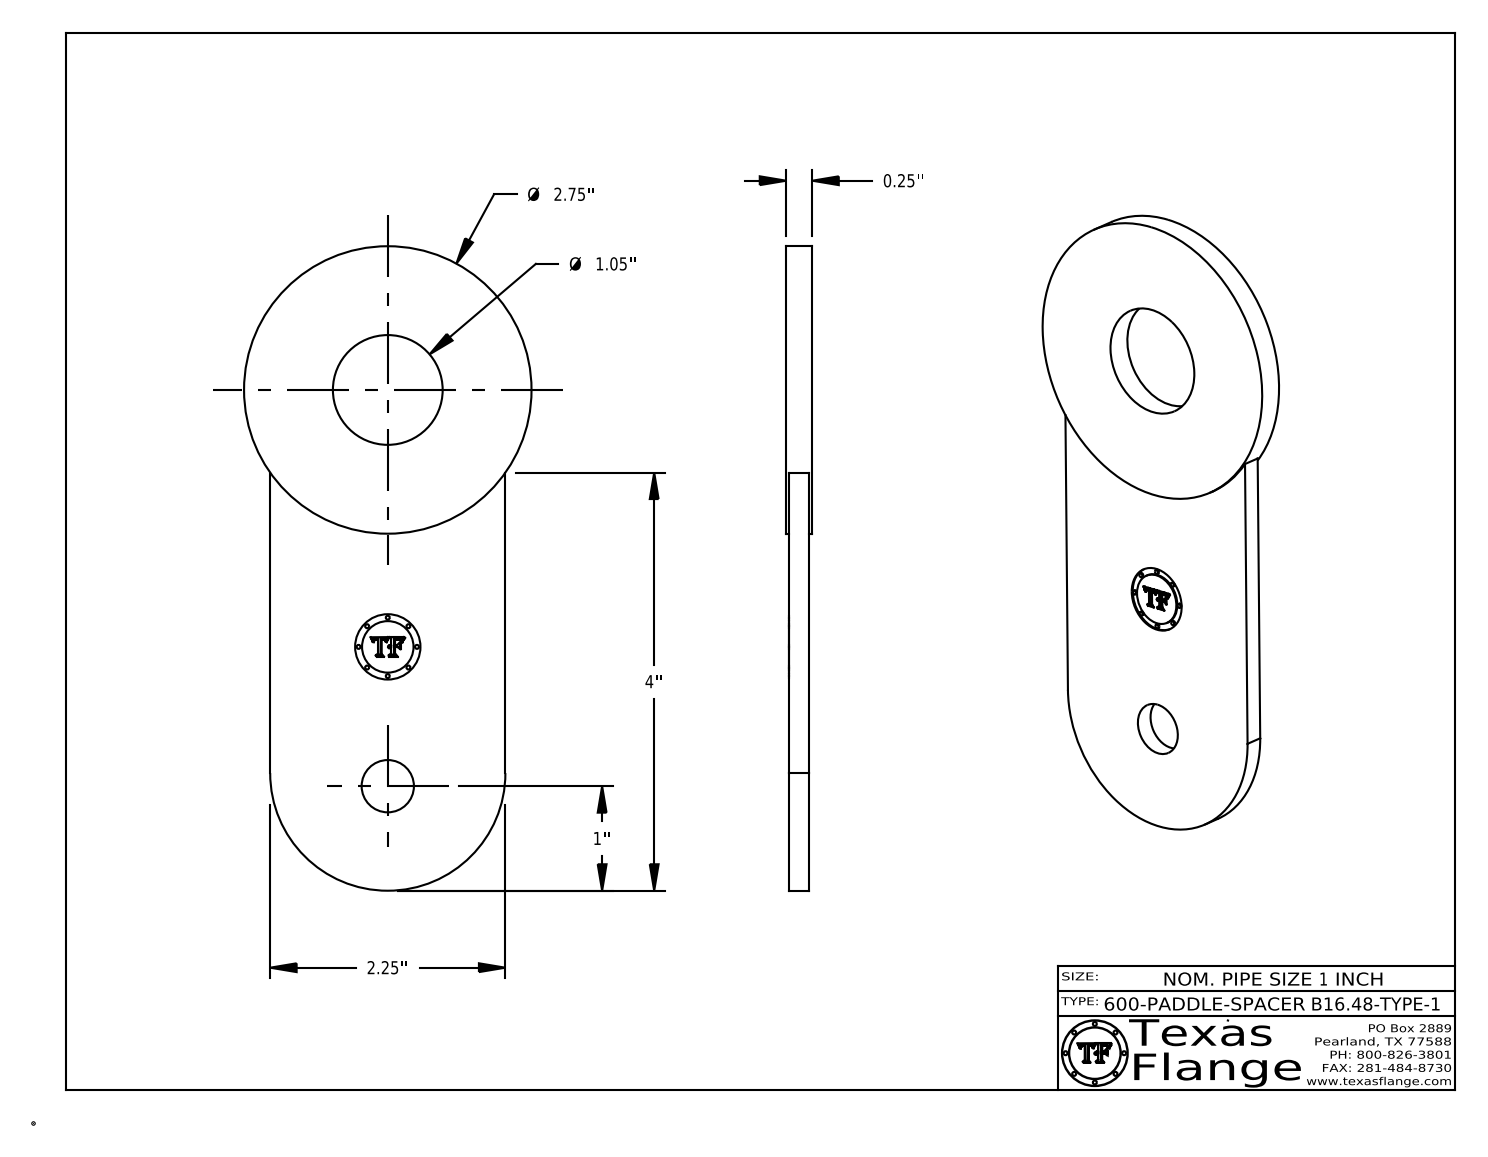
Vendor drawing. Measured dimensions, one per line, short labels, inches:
name: 1-600-PADDLE-SPACER-B16.48-TYPE-2
written by: CATIA V5 STEP AP214 (AUTOMOTIVE_DESIGN)
unit: in
bodies: 1 solid, 398 faces (371 planar, 27 cylindrical, 0 other)
size: 6.166 × 2.75 × 0.25
volume: 2.642 in³; area: 29.47 in²
holes: 1× ⌀0.5, 1× ⌀0.625, 1× ⌀1.05
bosses: 8× ⌀0.038, 1× ⌀2.75, 1× ⌀0.492
rounds: 1× R1.125
face distances: 0.219, 0.031, 0.187, 0.25, 2.25, 0.204, 0.172, 0.015, 0.046, 1.062
hole spacings: 1.333, 2.458, 3.791
